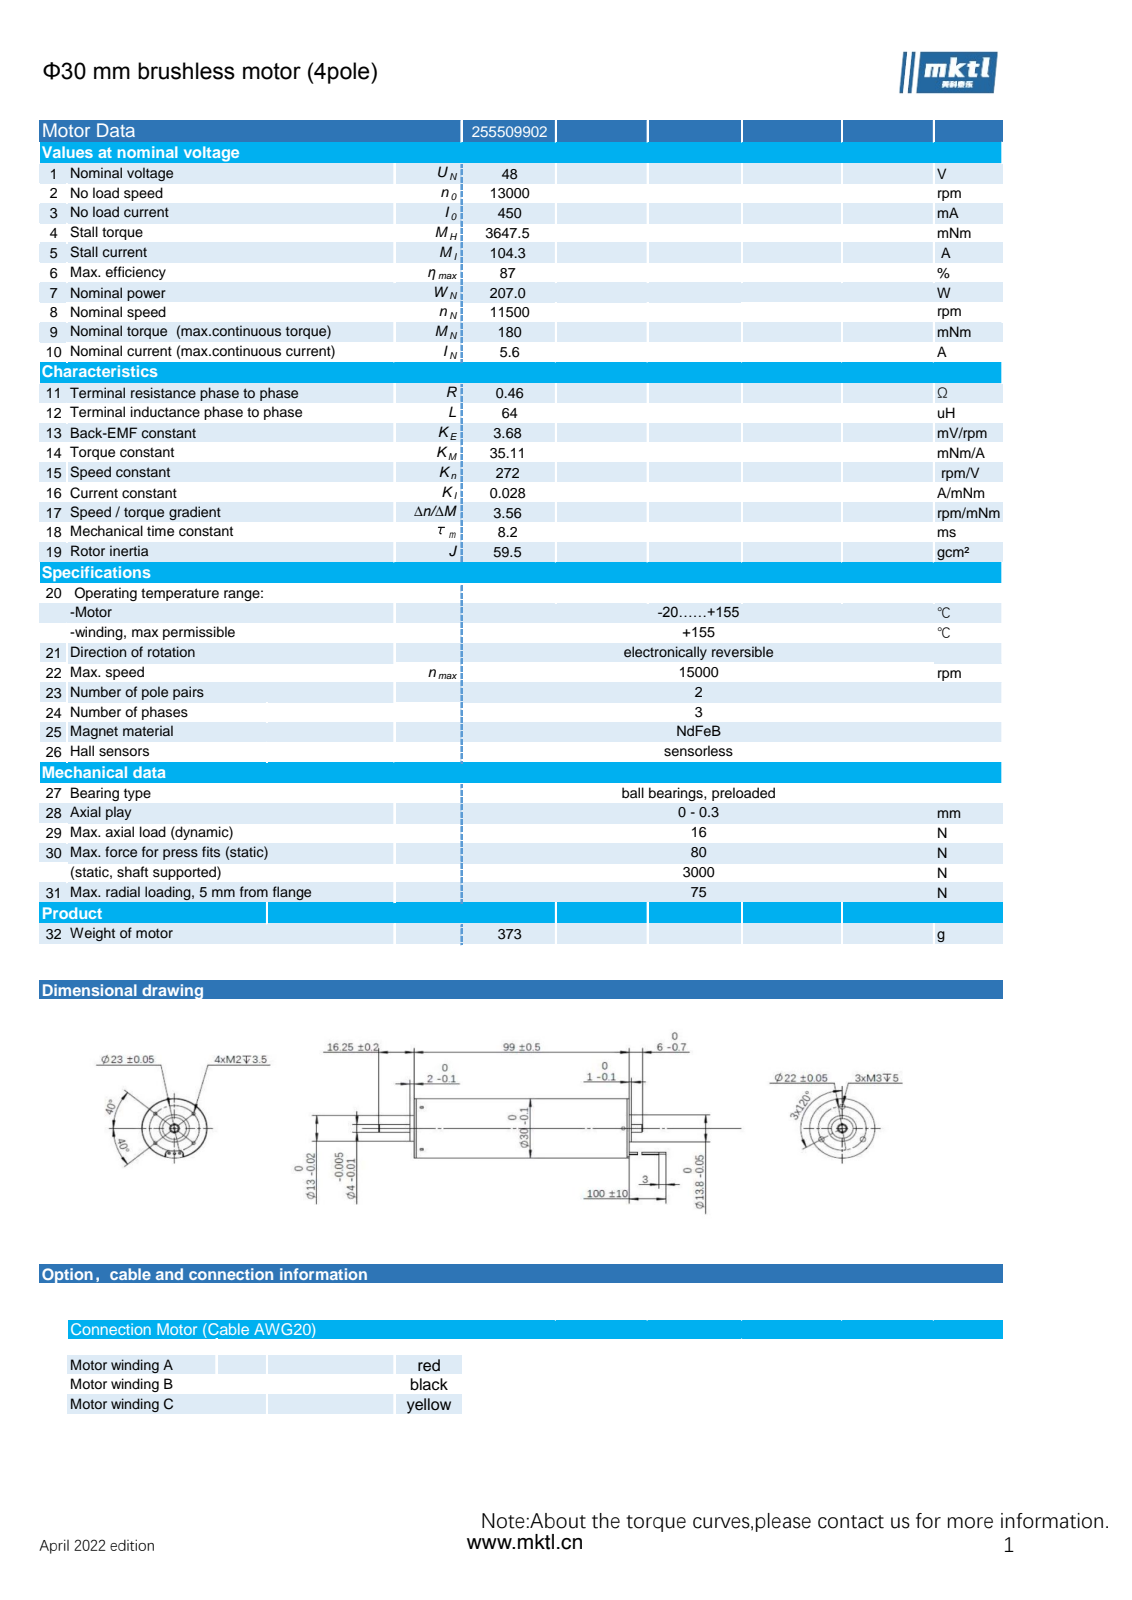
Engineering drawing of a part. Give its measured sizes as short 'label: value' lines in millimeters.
name: approval 255509901
written by: SolidWorks 2018 (CONFIG_CONTROL_DESIGN)
unit: mm
bodies: 434 solids, 3089 faces (943 planar, 2044 cylindrical, 102 other)
size: 131.85 × 30 × 30
volume: 64 781 mm³; area: 233 326 mm²
holes: 8× ⌀1.6, 3× ⌀1.8, 3× ⌀2.5, 1× ⌀4, 1× ⌀10, 1× ⌀11, 1× ⌀18.5, 1× ⌀19, 1× ⌀19.8, 1× ⌀23.3, 1× ⌀23.5
bosses: 6× ⌀1, 3× ⌀1.2, 3× ⌀0.8, 1× ⌀30, 1× ⌀28.5, 1× ⌀28.4, 1× ⌀28.1, 1× ⌀24
rounds: 24× R0.1, 21× R0.3, 12× R0.75, 12× R2, 7× R0.2, 7× R0.5, 6× R0.8, 2× R1.5
face distances: 0.4, 0.6, 1, 0.8, 1.2, 1.4, 76.4, 76.8, 1.6, 1.3
hole spacings: 11.5, 11, 12.75, 2.02, 2.44, 8.19, 9.52, 9.98
